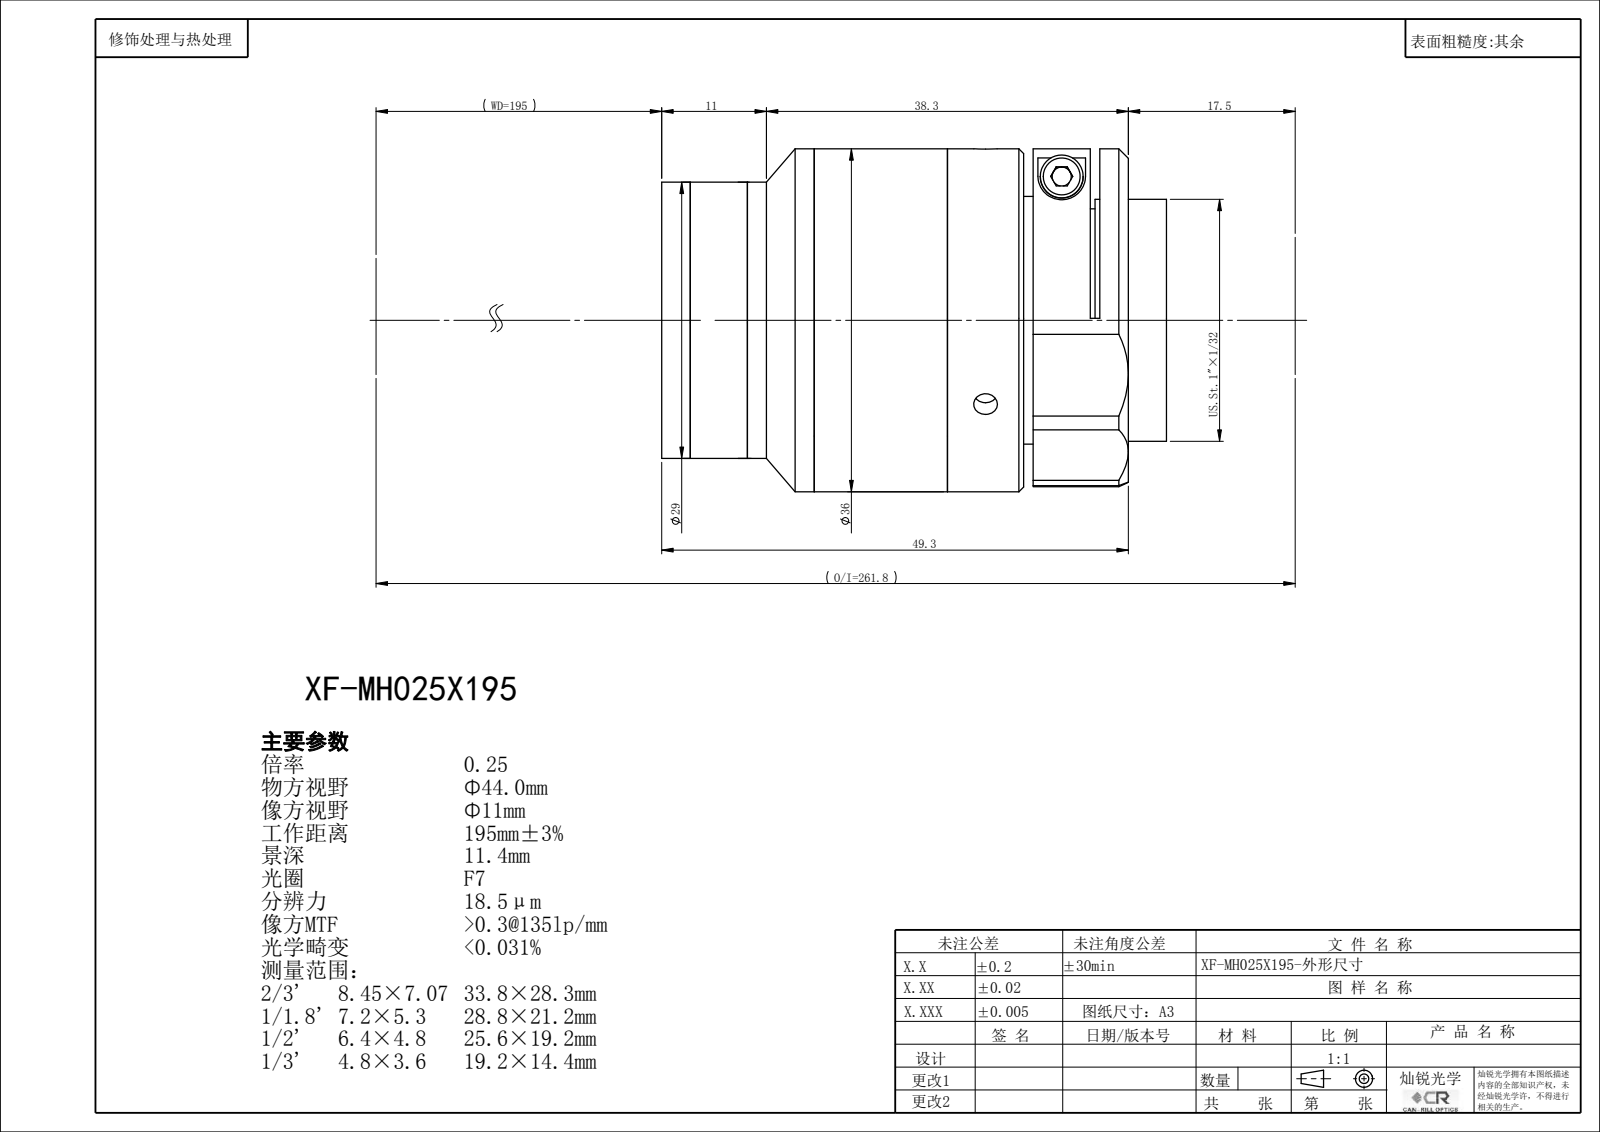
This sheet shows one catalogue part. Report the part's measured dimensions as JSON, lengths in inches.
{"part_name": "XF-MH025X195", "step_written_by": "SolidWorks 2022 (CONFIG_CONTROL_DESIGN)", "units": "inches", "bodies": {"solids": 0, "faces": 122, "planar": 60, "cylindrical": 46, "other": 16}, "overall_size": [2.1, 1.417, 1.417], "round_holes": [[0.098, 6], [0.551, 1], [0.882, 1], [0.945, 1], [0.98, 1], [1.039, 1], [1.063, 1]], "round_bosses_or_shafts": [[1.417, 1], [1.339, 1], [1.142, 1], [1, 1]], "face_to_face_distances": [0.761, 1.032, 1.793, 0.059, 1.734, 0.702, 0.481, 0.551, 1.253, 1.312], "hole_center_spacings": [0.374]}
